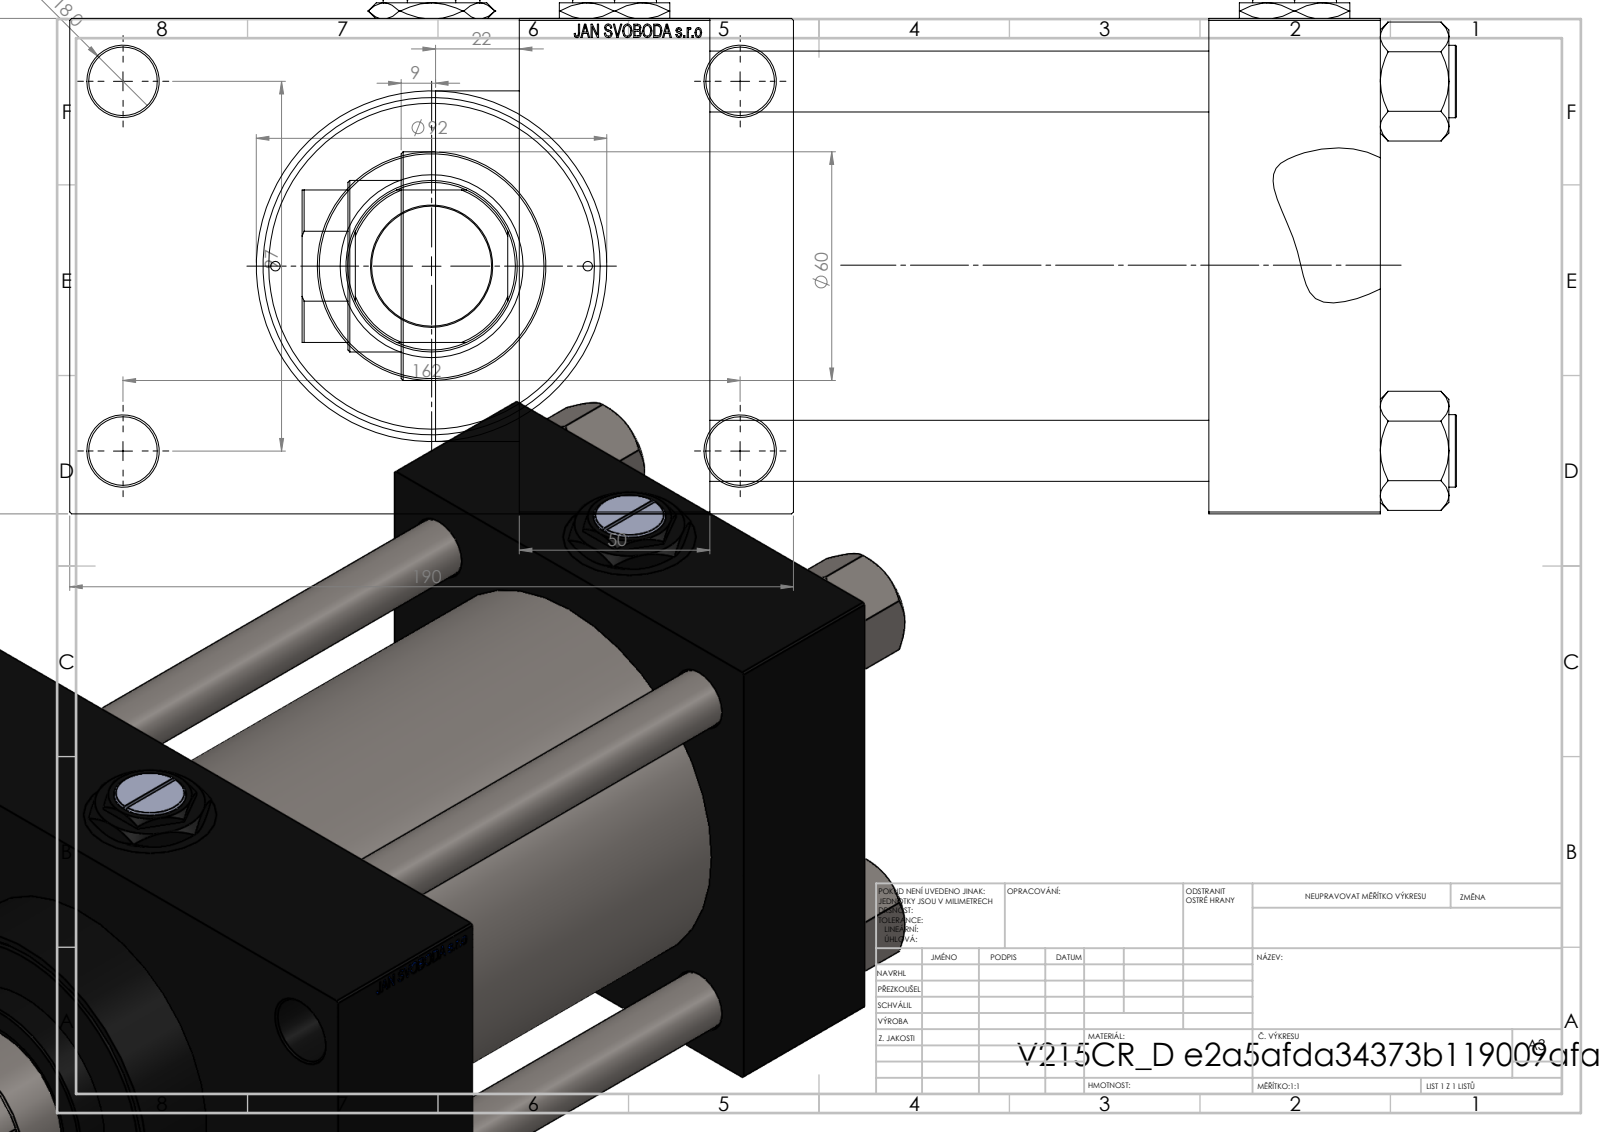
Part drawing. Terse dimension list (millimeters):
name: V215CR_D_Body; V215_VC_A; V215CR_VCP_D; V215CR_D_TYCINKA (+2 more)
written by: SolidWorks 2019 (CONFIG_CONTROL_DESIGN)
unit: mm
bodies: 13 solids, 1260 faces (595 planar, 103 cylindrical, 562 other)
size: 303 × 190 × 137
volume: 2 778 000 mm³; area: 421 017 mm²
holes: 4× ⌀16, 4× ⌀18, 4× ⌀26.44, 4× ⌀35, 3× ⌀7, 2× ⌀2.5, 1× ⌀31.5, 1× ⌀45, 1× ⌀48, 1× ⌀76, 1× ⌀85.5, 1× ⌀100
bosses: 4× ⌀19, 1× ⌀106, 1× ⌀92, 1× ⌀60
rounds: 1× R22
face distances: 130, 45, 176, 131, 226, 181, 50, 30, 160, 80
hole spacings: 32.55, 49.02, 62.87, 68.52, 94.41, 96.9, 101.73, 102.27
